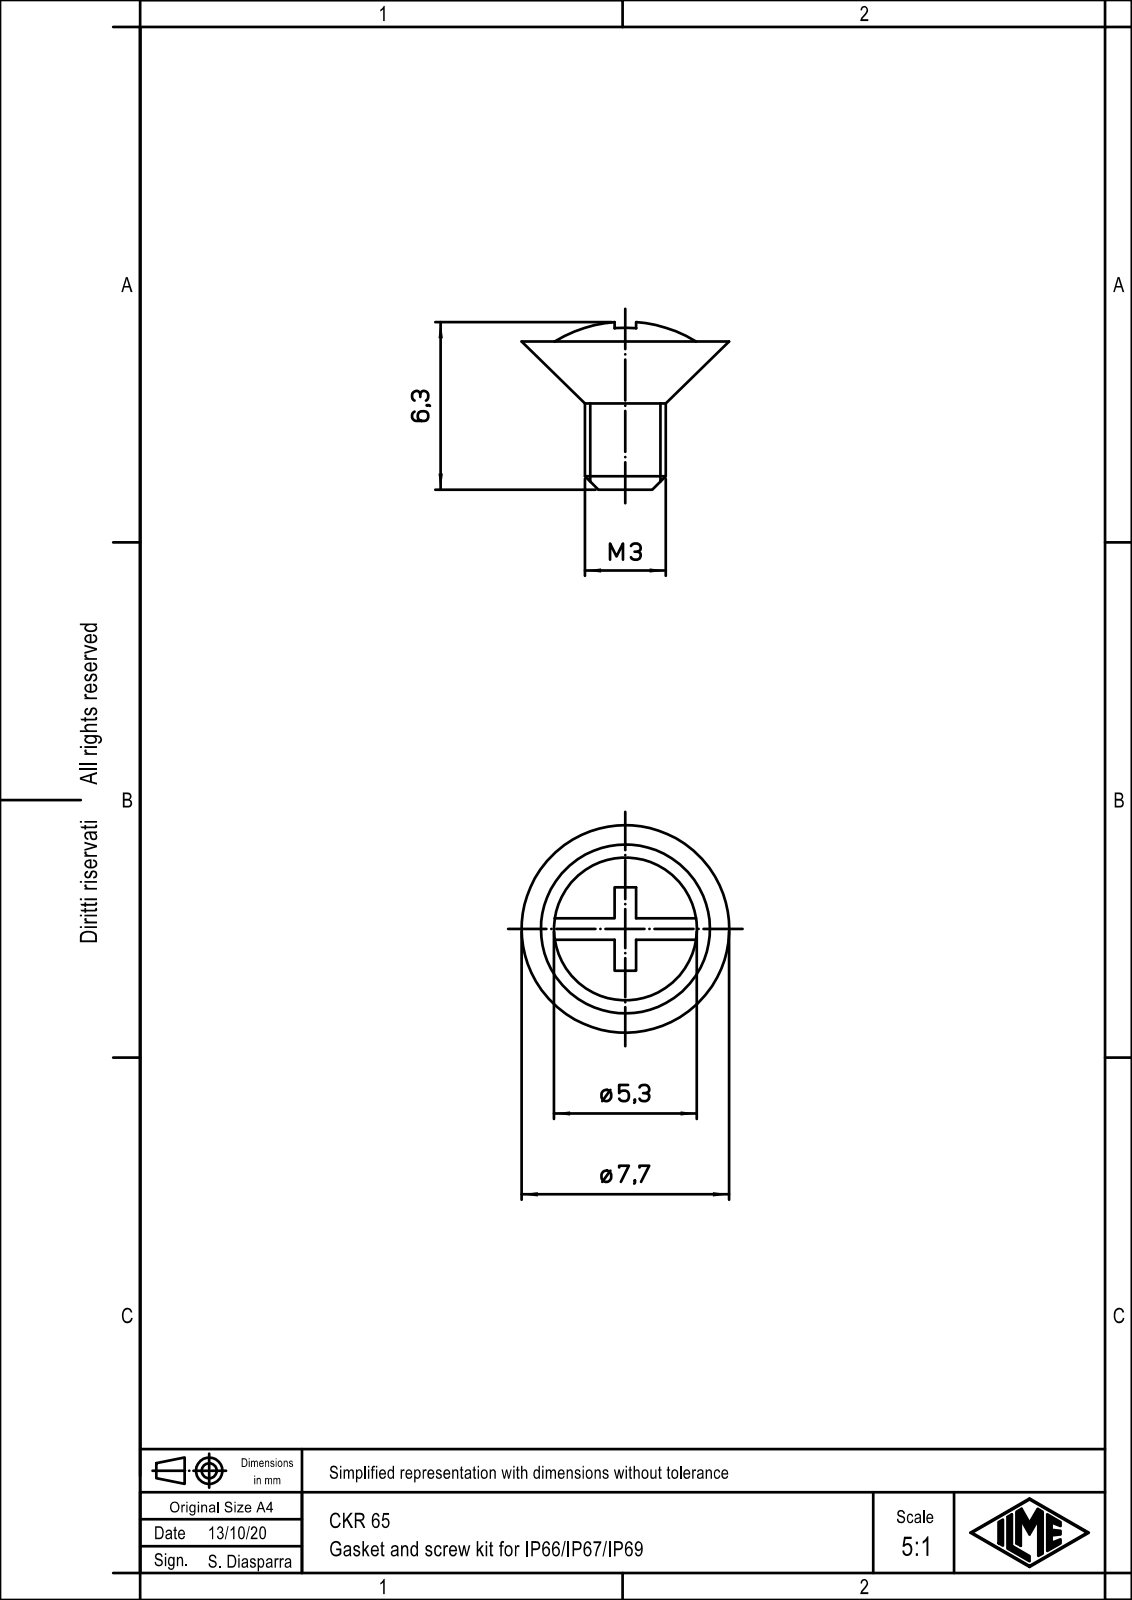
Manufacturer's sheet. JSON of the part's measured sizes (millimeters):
{"part_name": "CKR_65", "step_written_by": "OneSpace Modeling 15.50B 03-Nov-2007 (C) CoCreate Software GmbH (AUTOMOTIVE_DESIGN)", "units": "millimeters", "bodies": {"solids": 1, "faces": 60, "planar": 26, "cylindrical": 4, "other": 30}, "overall_size": [7.7, 7.7, 6.19], "volume_mm3": 77, "surface_area_mm2": 174, "round_bosses_or_shafts": [[5.6, 1], [3.2, 1]], "face_to_face_distances": [5.5, 4.73, 0.77, 0.8, 2.55, 2.18, 2.95, 5.33, 2.78, 0.6]}
